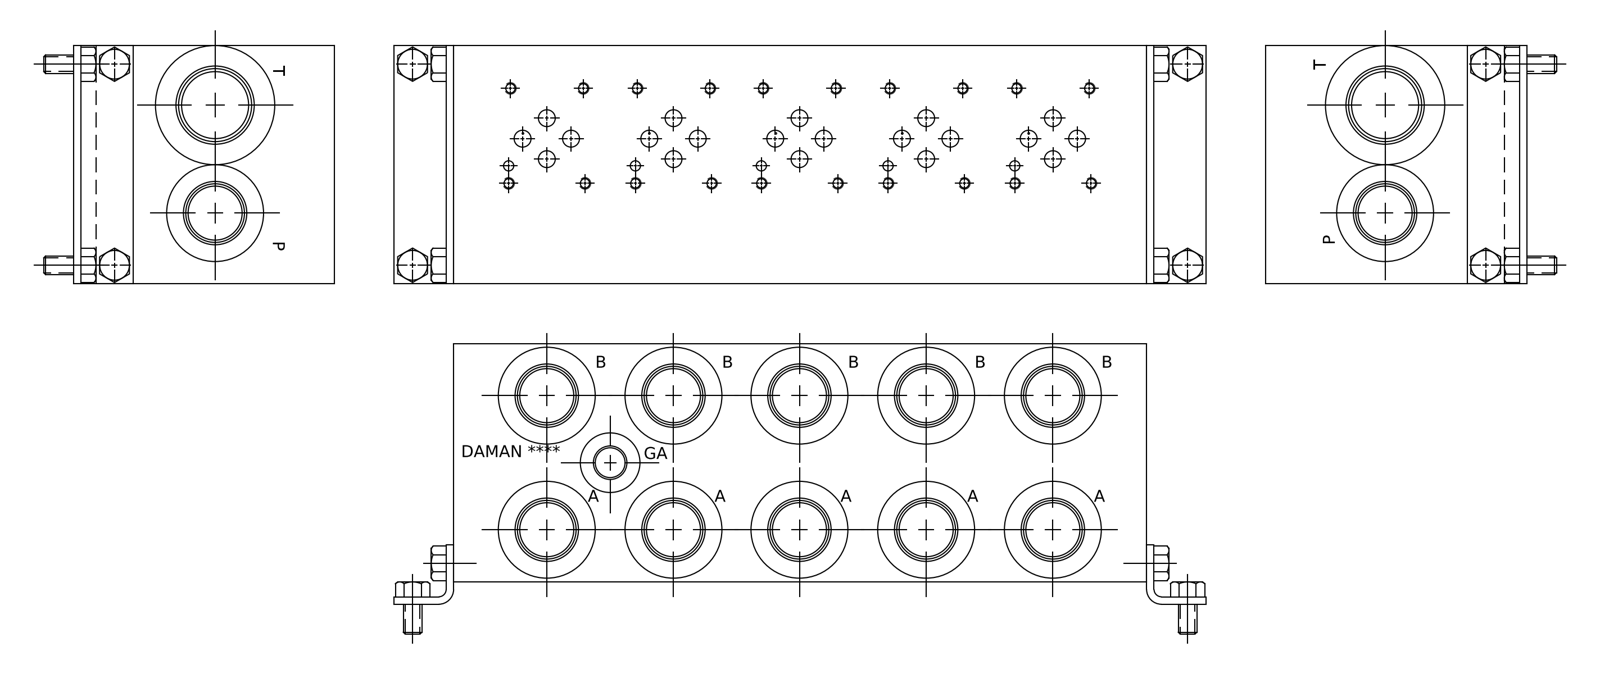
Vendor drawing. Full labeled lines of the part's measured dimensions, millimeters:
Part name (STEP PRODUCT): Part__D03HP052S_3D
STEP written by: Autodesk Inventor 2020 (AUTOMOTIVE_DESIGN)
Units: millimetres
Bodies: 1 solid, 944 faces (467 planar, 154 cylindrical, 323 other)
Overall size (bounding box): 295.27 × 101.6 × 101.6
Volume: 2 761 000 mm³ · Surface area: 187 283 mm²
Round holes (diameter × count): ⌀3.78 ×20, ⌀4.83 ×20, ⌀6.35 ×15, ⌀23.01 ×11, ⌀24.92 ×11, ⌀27.43 ×11, ⌀42.04 ×11, ⌀27 ×9, ⌀3.96 ×5, ⌀7.14 ×5, ⌀10.72 ×5, ⌀26.99 ×3
Main face-to-face distances: 101.6, 0.79, 100.81, 295.27, 294.49, 0.78, 293.7, 294.48, 19.05, 19.84
Hole centre spacings: 107.95, 53.98, 53.97, 13.52, 13.54, 78.61, 161.92, 161.93
